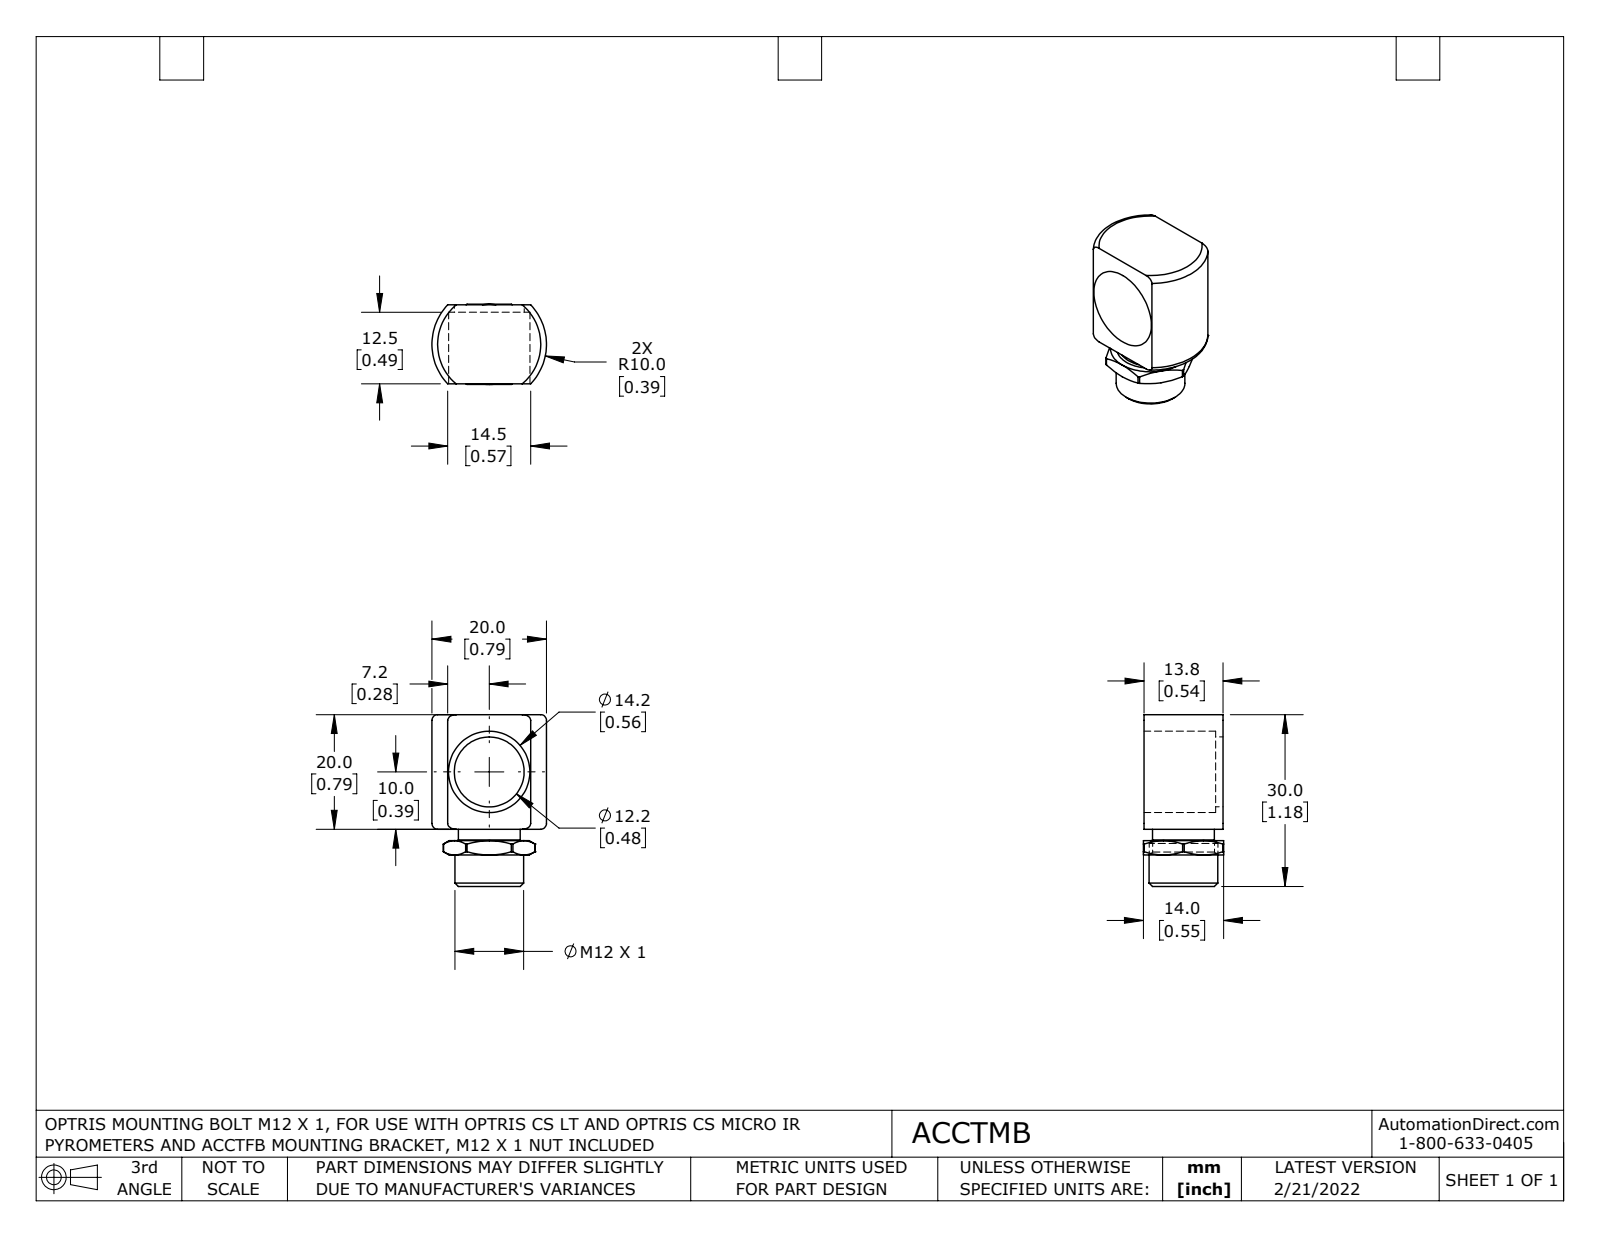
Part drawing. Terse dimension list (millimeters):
name: ACCTMB - Mounting bolt with thread nc fxt Coord
written by: SolidWorks 2021 (AUTOMOTIVE_DESIGN)
unit: mm
bodies: 2 solids, 56 faces (14 planar, 18 cylindrical, 24 other)
size: 30 × 20 × 14
volume: 4 160 mm³; area: 2 750 mm²
holes: 1× ⌀10.8, 1× ⌀12.2, 1× ⌀14.2
bosses: 1× ⌀12
rounds: 1× R8, 1× R10
face distances: 13.8, 20, 30, 10, 14, 22, 24.5, 2, 4.5, 2.5
